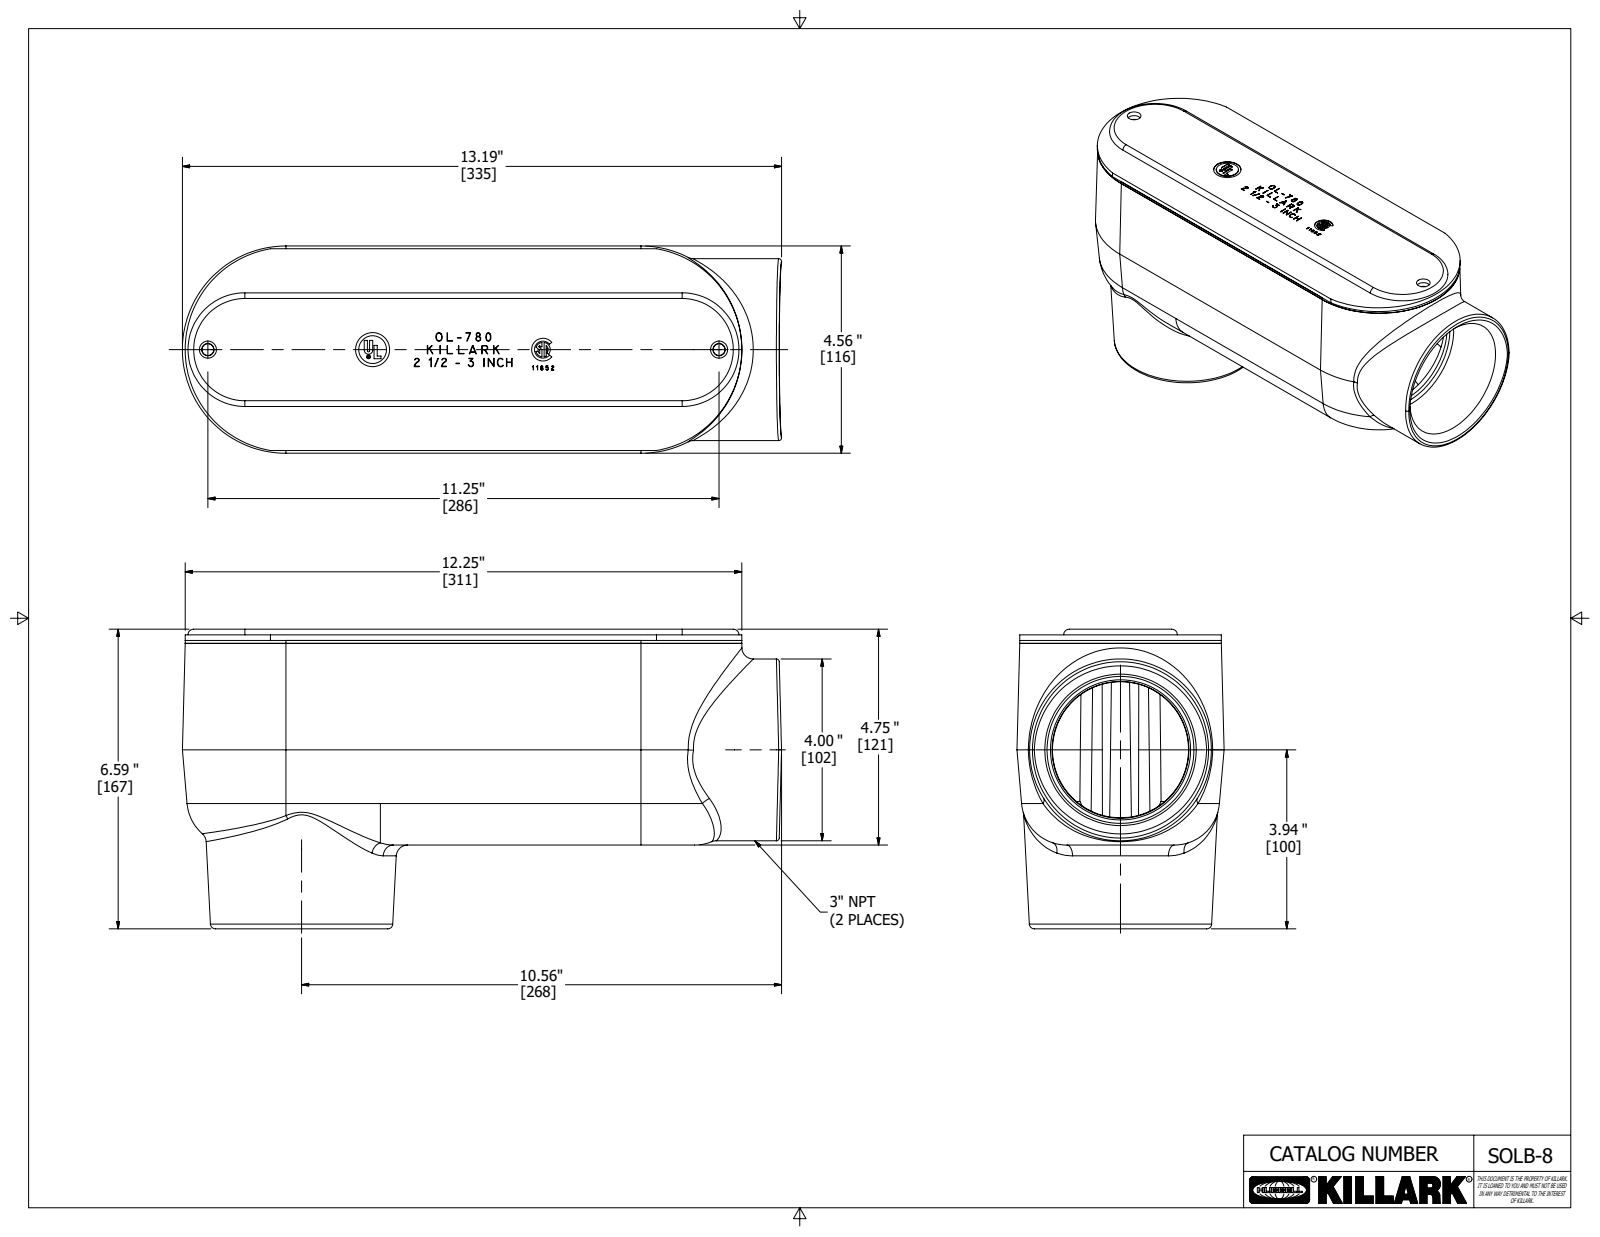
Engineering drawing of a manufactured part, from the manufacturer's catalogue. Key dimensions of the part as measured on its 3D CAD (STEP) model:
Part name (STEP PRODUCT): SOLB-8; 17325-3; 03644; 0243875B
STEP written by: Autodesk Inventor 2020 (AUTOMOTIVE_DESIGN)
Units: inches
Bodies: 3 solids, 1814 faces (830 planar, 69 cylindrical, 915 other)
Overall size (bounding box): 13.186 × 6.594 × 4.56
Volume: 56.5 in³ · Surface area: 586.3 in²
Round holes (diameter × count): ⌀0.259 ×2, ⌀0.375 ×2, ⌀0.07 ×1, ⌀0.083 ×1, ⌀0.611 ×1, ⌀0.75 ×1
Round bosses / shafts (diameter × count): ⌀4 ×1, ⌀0.75 ×1, ⌀0.611 ×1, ⌀0.083 ×1, ⌀0.07 ×1
Partial cylindrical surfaces — rounded edges, fillets, slot ends (radius × count): R0.062 ×10, R0.125 ×4, R0.25 ×3, R0.008 ×2, R0.013 ×2, R0.024 ×2, R0.094 ×2, R1 ×2
Main face-to-face distances: 0.063, 0.125, 0.187, 0.125, 0.25, 0.313, 4.469, 4.281, 4.344, 4.594
Hole centre spacings: 0.183, 2, 5.625, 1.917, 2.096, 3.539, 3.625, 5.537
